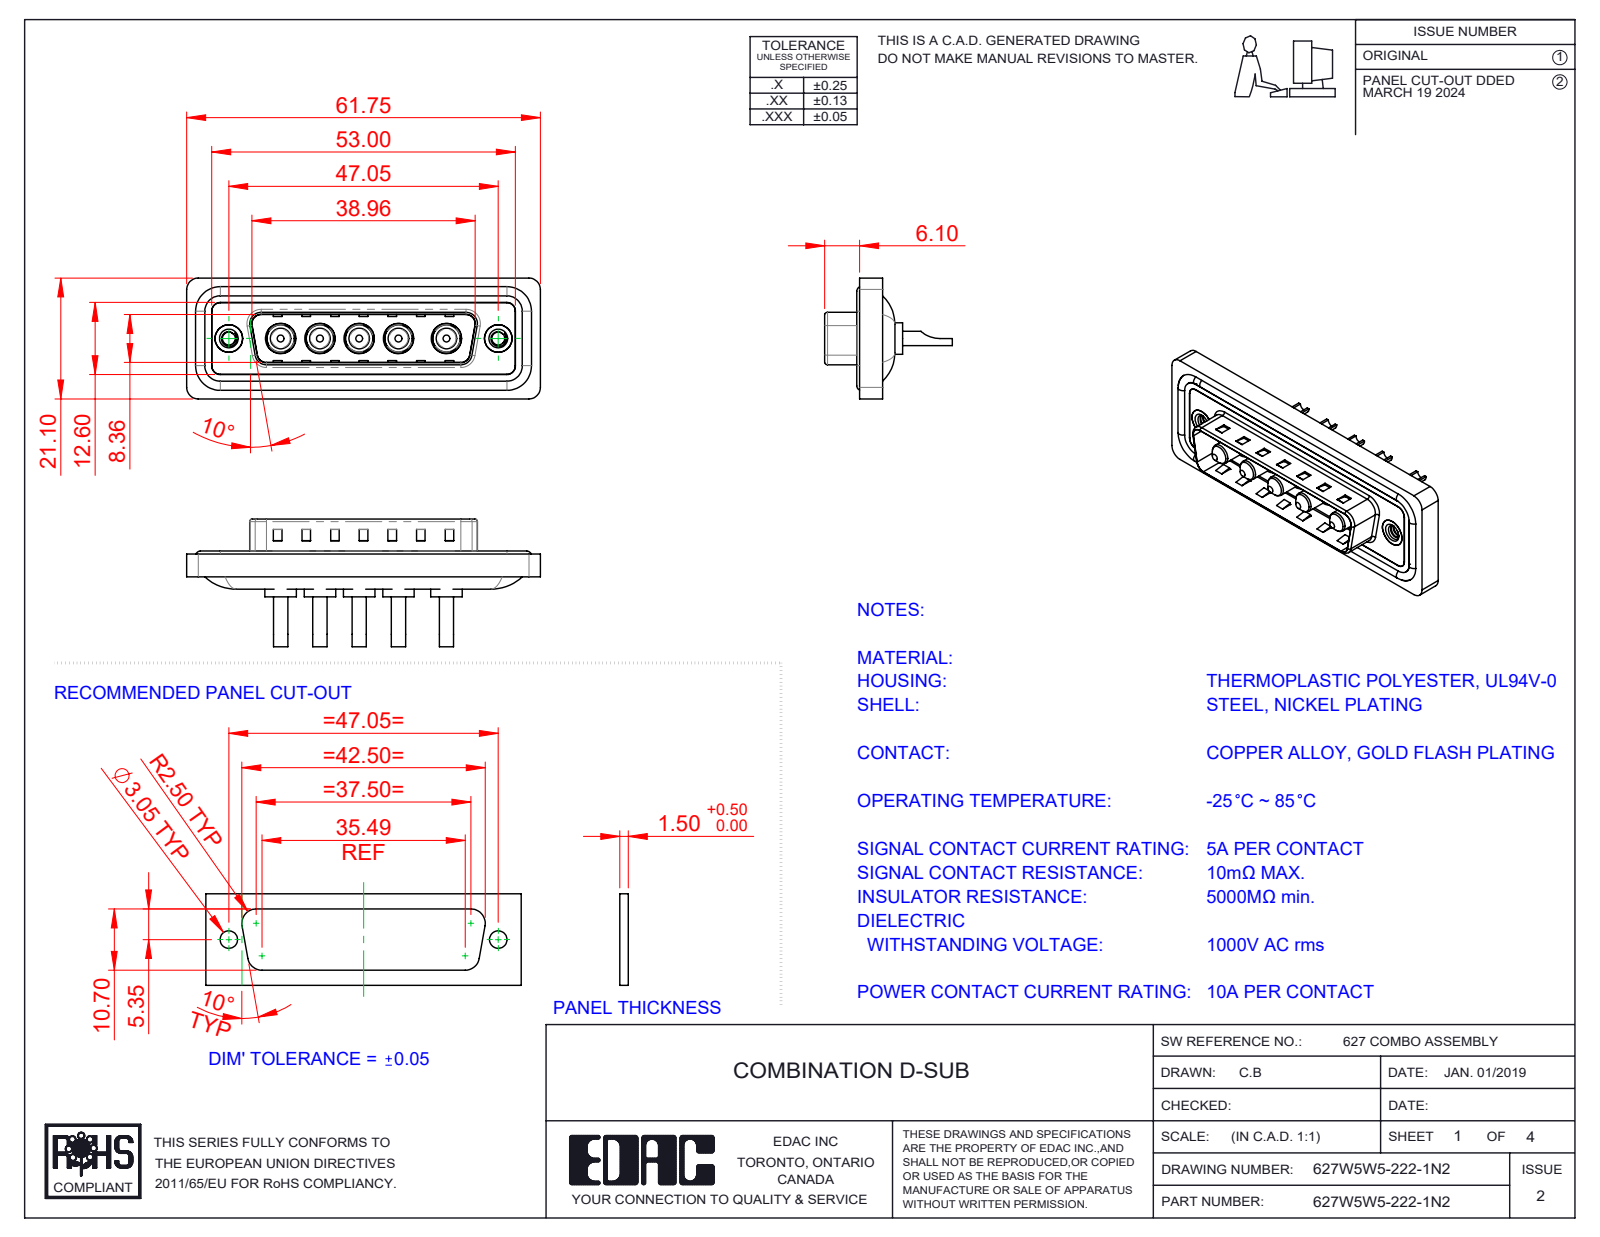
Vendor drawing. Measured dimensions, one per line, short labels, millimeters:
name: Power Pin_10A SC; 627W5W5-222-1N2; 627Combo Shell Rear_25 Contacts; 627Combo Waterproof Housing_25 Contacts (+3 more)
written by: SolidWorks 2023 (CONFIG_CONTROL_DESIGN)
unit: mm
bodies: 17 solids, 708 faces (269 planar, 298 cylindrical, 141 other)
size: 61.75 × 22.3 × 21.1
volume: 7 459 mm³; area: 12 035 mm²
holes: 5× ⌀1.7, 5× ⌀4.85, 5× ⌀5.3, 2× ⌀2.26, 2× ⌀4, 2× ⌀4.8, 2× ⌀5
bosses: 5× ⌀5.5, 5× ⌀5.2, 5× ⌀4.75, 5× ⌀3.75, 5× ⌀3.6, 5× ⌀2.5, 4× ⌀1.6, 2× ⌀4.9
rounds: 22× R1.5, 18× R2, 8× R0.5, 8× R1.6, 5× R2.1, 4× R0.25, 4× R0.6, 4× R0.65
face distances: 0.4, 1.5, 0.5, 1.1, 3.1, 1.6, 2.9, 0.82, 9.58, 5.65
hole spacings: 6.86, 9.04, 13.73, 38.01, 6.87, 8.37, 8.38, 9.05
